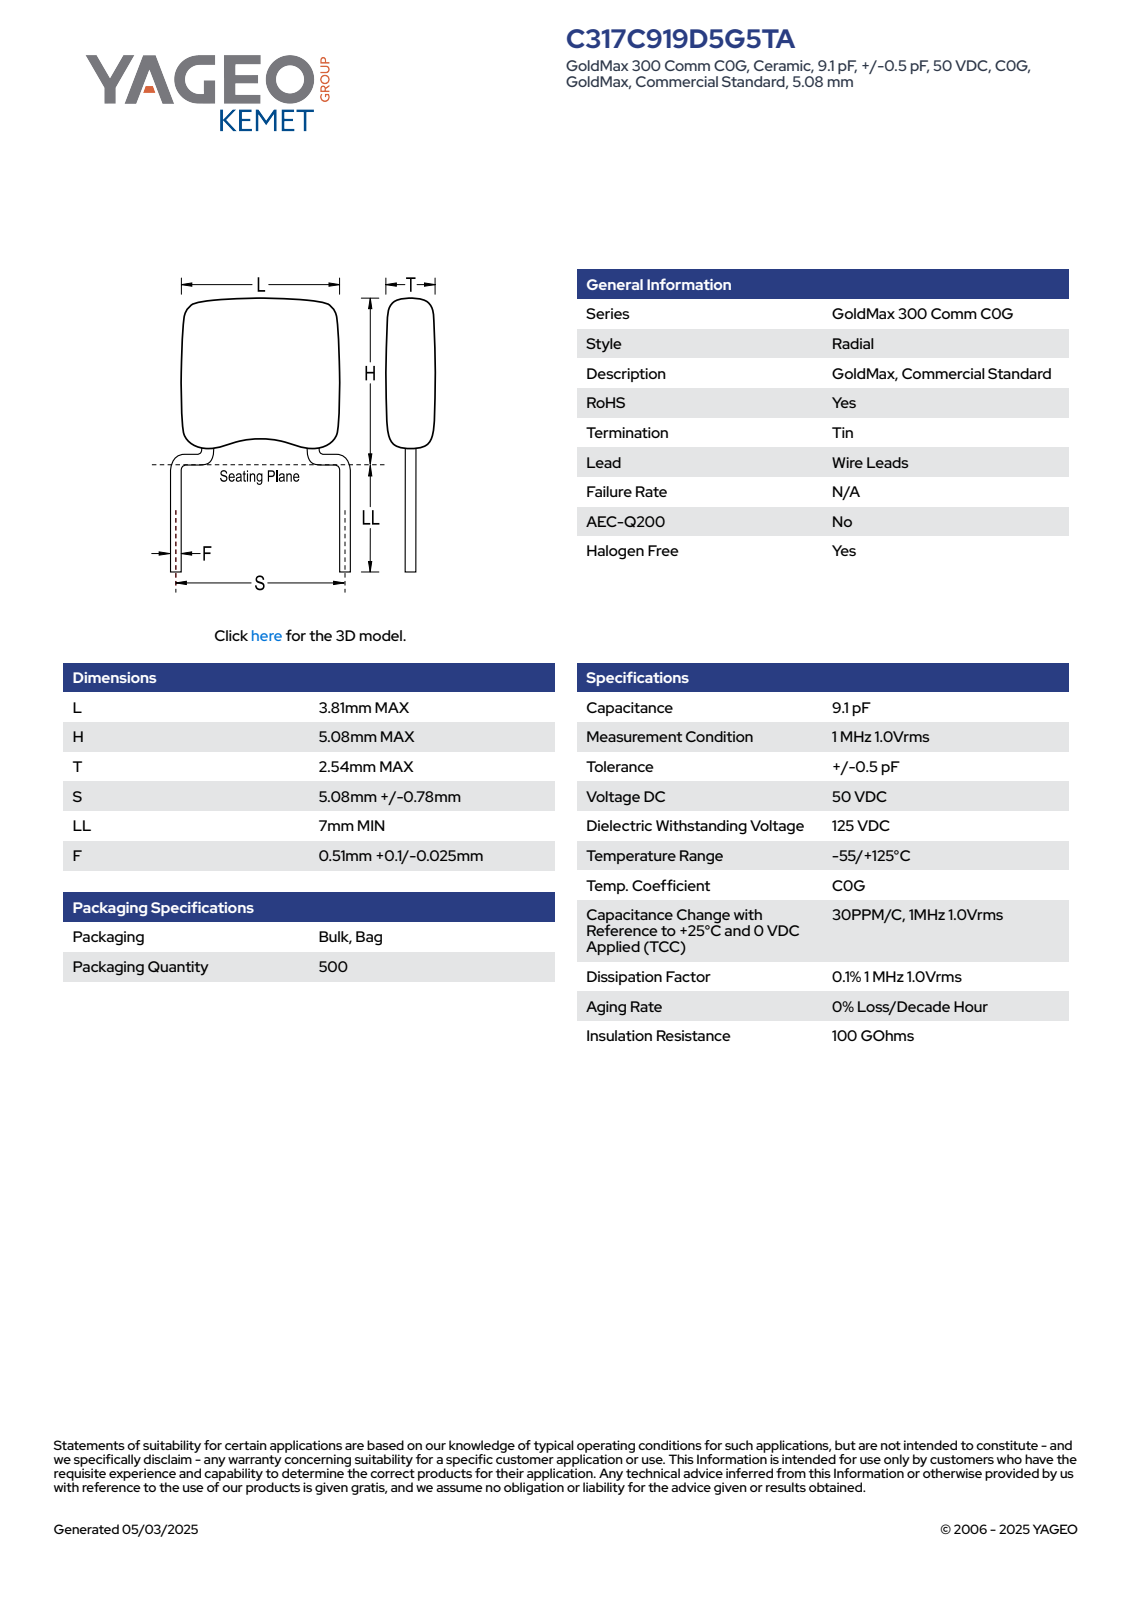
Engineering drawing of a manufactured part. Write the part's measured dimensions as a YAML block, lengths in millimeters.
part_name: "CCR_SB_3.81X5.08_L3.81H5.08T2.54S5.08LL7F0.51"
step_written_by: "SolidWorks 2014 (AUTOMOTIVE_DESIGN)"
units: millimeters
bodies: {solids: 4, faces: 97, planar: 65, cylindrical: 14, other: 18}
overall_size: [12.08, 5.59, 2.54]
volume: 32
surface_area: 79
round_bosses_or_shafts:
  - {diameter: 0.51, count: 2}
partial_cylinders:
  - {radius: 1, count: 10}
face_to_face_distances: [2.54, 3.81, 3.61, 0.32, 1.98, 1.63, 1.66, 1.95, 0.41, 1.32]
